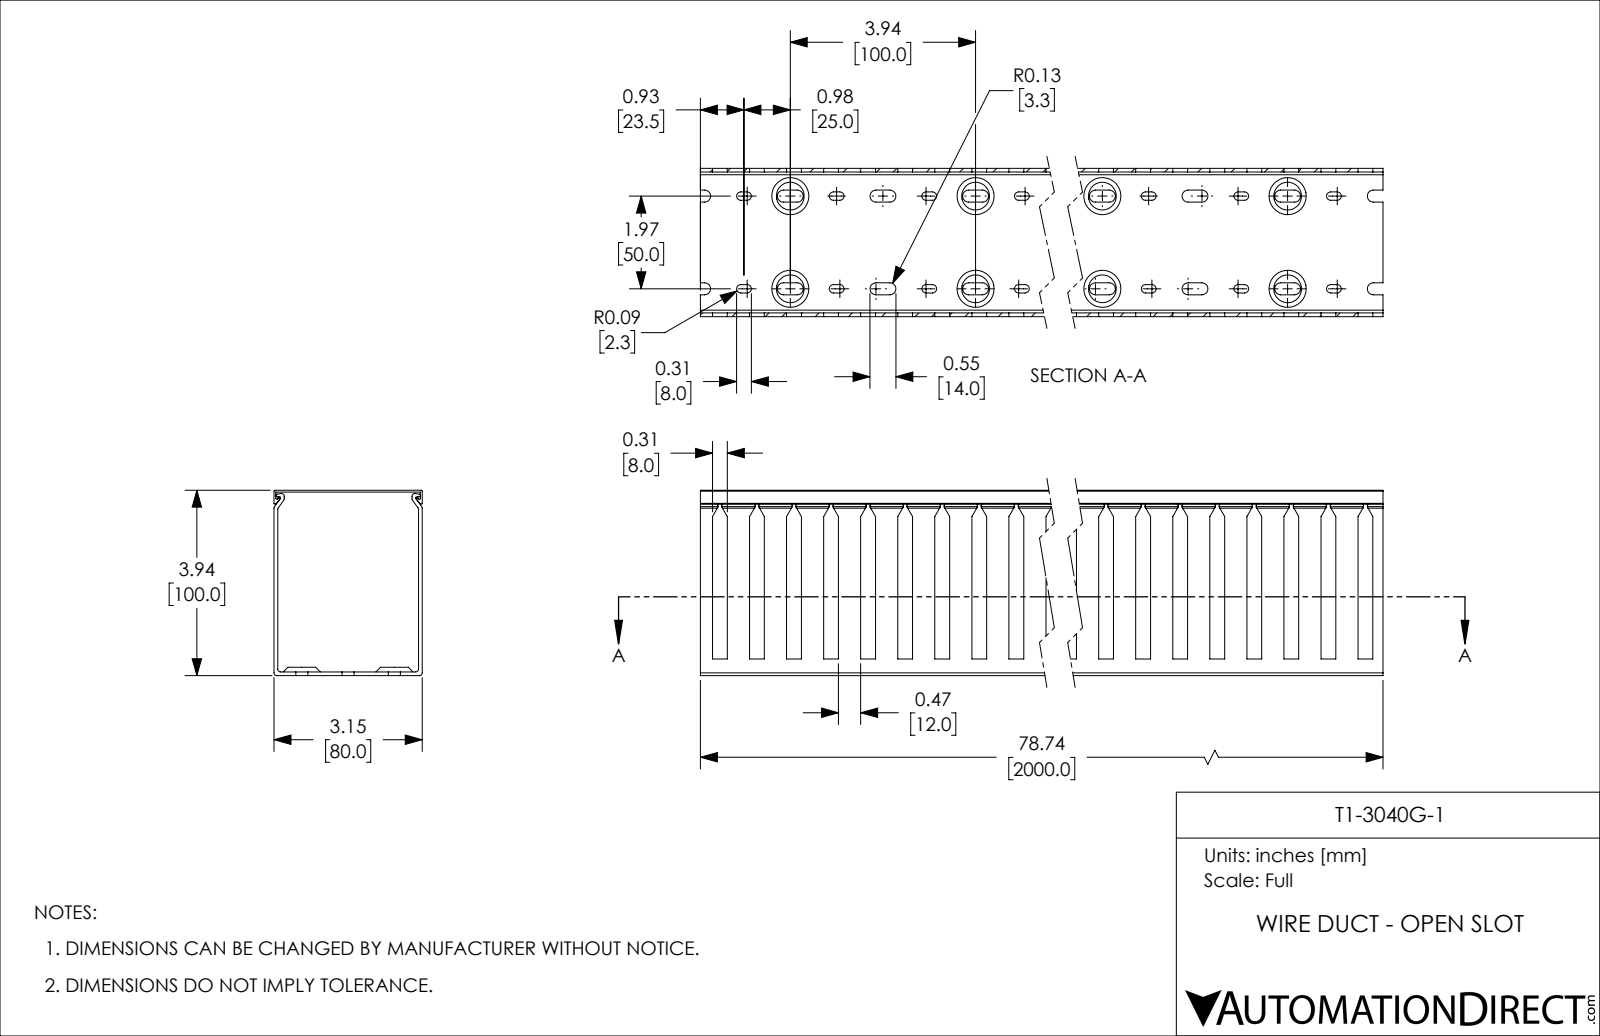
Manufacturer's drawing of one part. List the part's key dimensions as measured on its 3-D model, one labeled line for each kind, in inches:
Part name (STEP PRODUCT): T1-3040K-1
STEP written by: SolidWorks 2021 (CONFIG_CONTROL_DESIGN)
Units: inches
Bodies: 2 solids, 1573 faces (762 planar, 731 cylindrical, 80 other)
Overall size (bounding box): 78.74 × 3.937 × 3.15
Volume: 77.99 in³ · Surface area: 2 292 in²
Partial cylindrical surfaces — rounded edges, fillets, slot ends (radius × count): R0.128 ×200, R0.089 ×160, R0.059 ×12, R0.02 ×8, R0.03 ×6
Main face-to-face distances: 0.079, 3.071, 3.15, 0.039, 2.992, 3.937, 3.898, 3.819, 3.858, 3.11
